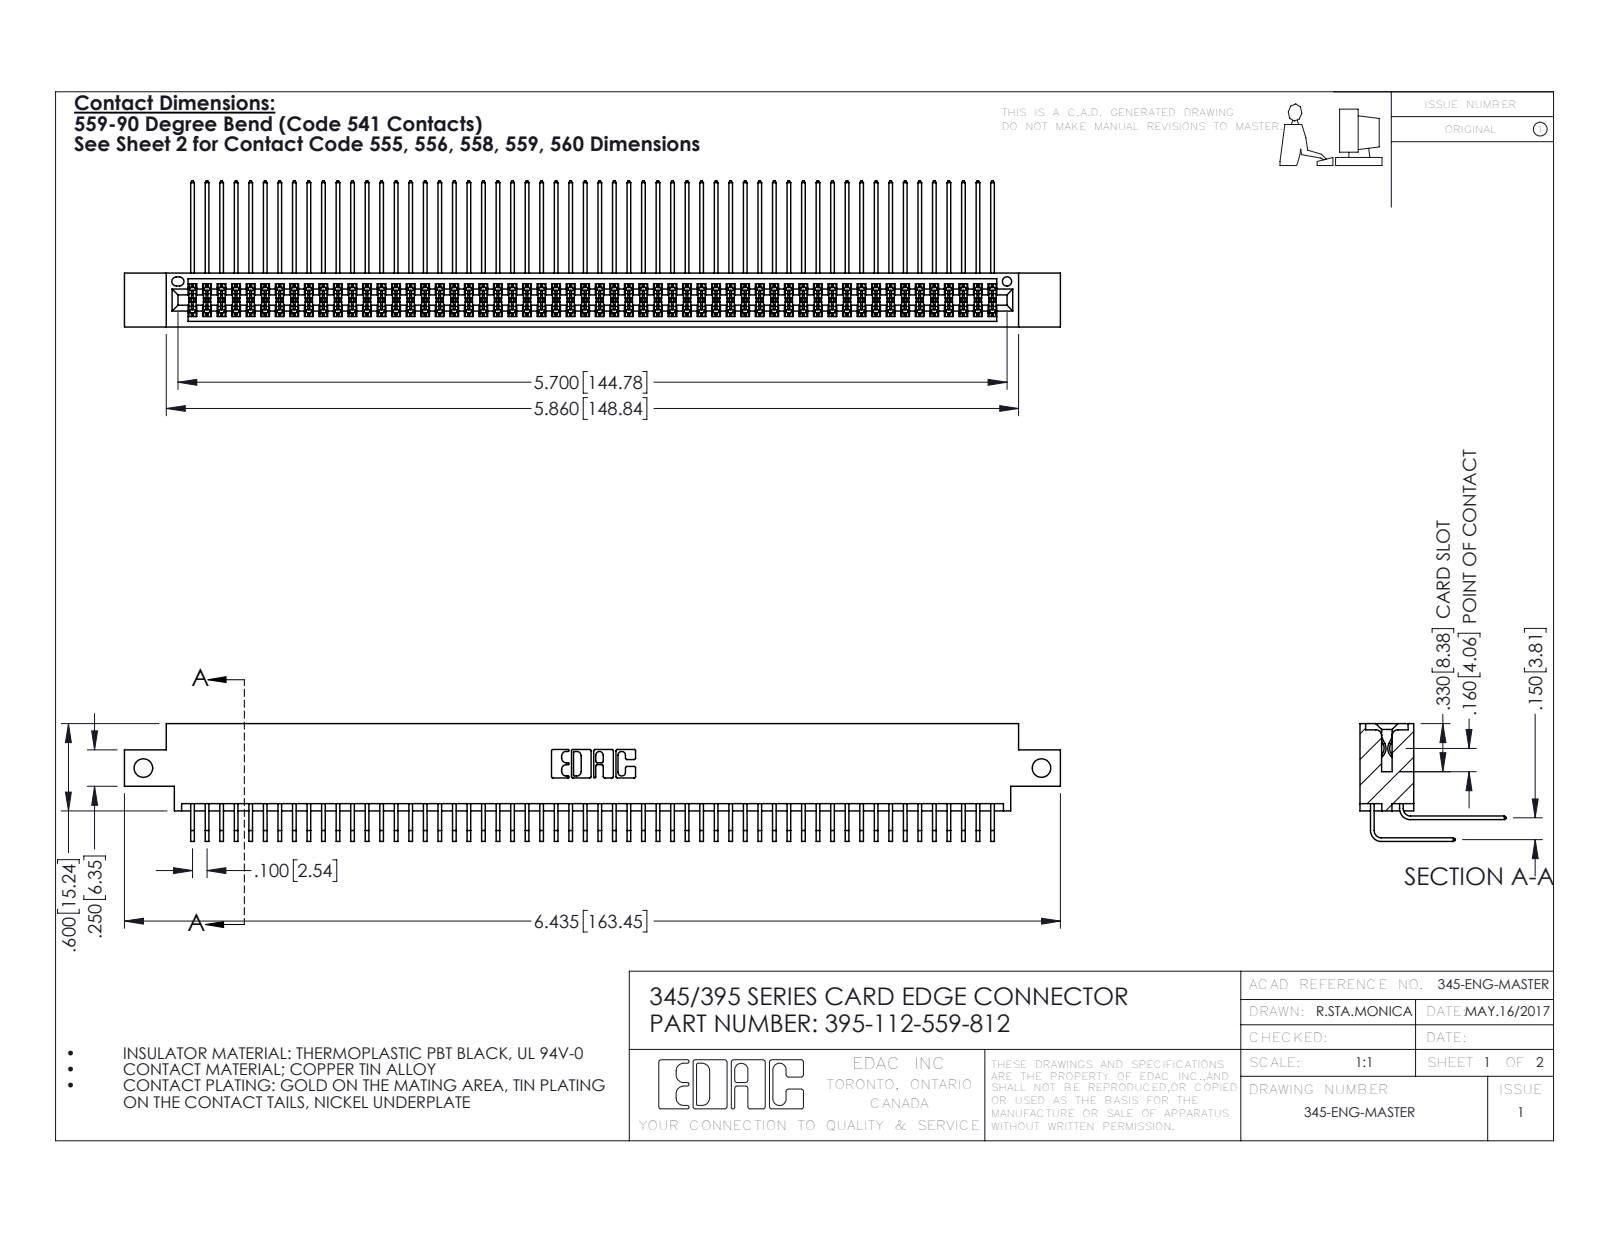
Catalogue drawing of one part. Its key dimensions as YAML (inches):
part_name: "345-292-001_559 Tail - 2; 345-292-001_558 559 Tail - 1; 345 Part_0.170 Offset - Side Mount; 395-112-559-812"
step_written_by: "SolidWorks 2016 (CONFIG_CONTROL_DESIGN)"
units: inches
bodies: {solids: 113, faces: 5954, planar: 4004, cylindrical: 1950, other: 0}
overall_size: [6.435, 1.005, 0.809]
volume: 1.004
surface_area: 42.84
round_holes:
  - {diameter: 0.128, count: 2}
  - {diameter: 0.064, count: 1}
partial_cylinders:
  - {radius: 0.006, count: 168}
  - {radius: 0.01, count: 22}
  - {radius: 0.007, count: 6}
  - {radius: 0.031, count: 6}
  - {radius: 0.026, count: 3}
  - {radius: 0.014, count: 2}
  - {radius: 0.019, count: 2}
  - {radius: 0.022, count: 2}
face_to_face_distances: [0.072, 0.298, 0.37, 0.2, 0.098, 0.272, 0.025, 0.225, 0.175, 0.15]
hole_center_spacings: [6.175]
